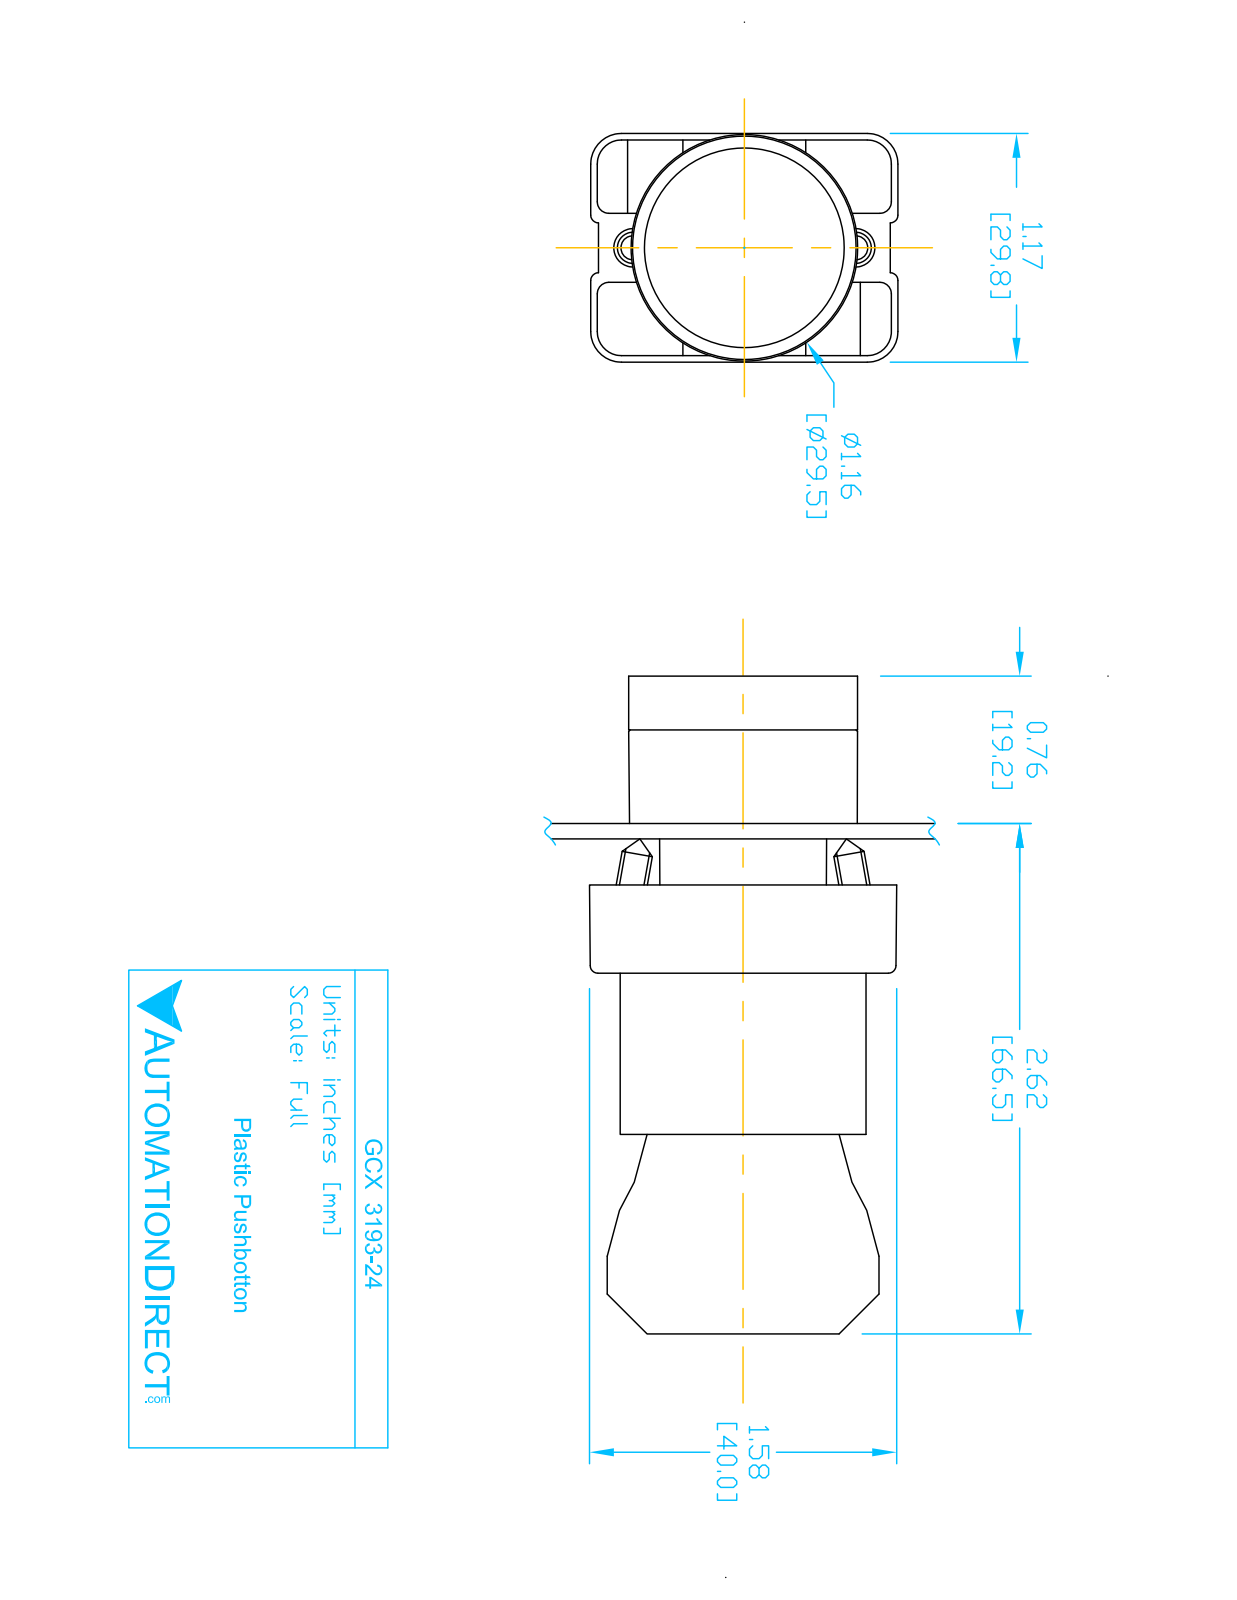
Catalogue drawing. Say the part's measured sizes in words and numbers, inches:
The part is named "GCX3193 OPERATOR; CONTACT BLOCK; ECX1050; GCX3193-24 (+1 more)". Its 3-D file was written by "SolidWorks 2016 (AUTOMOTIVE_DESIGN)". It is 8 solids with 431 faces: 252 planar, 148 cylindrical and 31 other. Overall it measures 3.319 by 1.581 by 1.177 inches. Its volume is 2.794 cubic inches and its surface area 38.77 square inches. Round holes: 2 of diameter 0.079, 2 of diameter 0.124, 2 of diameter 0.13, 1 of diameter 0.087, 1 of diameter 0.197, 1 of diameter 0.469, 1 of diameter 0.878, 1 of diameter 0.888, 1 of diameter 1.024. Round bosses or shafts: 4 of diameter 0.157, 1 of diameter 1.175, 1 of diameter 1.004, 1 of diameter 0.945, 1 of diameter 0.856, 1 of diameter 0.78, 1 of diameter 0.504. Partial cylindrical surfaces (rounded edges, fillets, slot ends): 24 of radius 0.059, 12 of radius 0.041, 12 of radius 0.124, 12 of radius 0.157, 8 of radius 0.039, 2 of radius 0.128, 1 of radius 0.02, 1 of radius 0.063. The main face-to-face distances are 0.827, 0.579, 2.02, 1.193, 1.171, 0.276, 2.295, 1.469, 0.031, 0.033. The hole center spacings are 0.236, 0.544, 0.472, 0.49.
